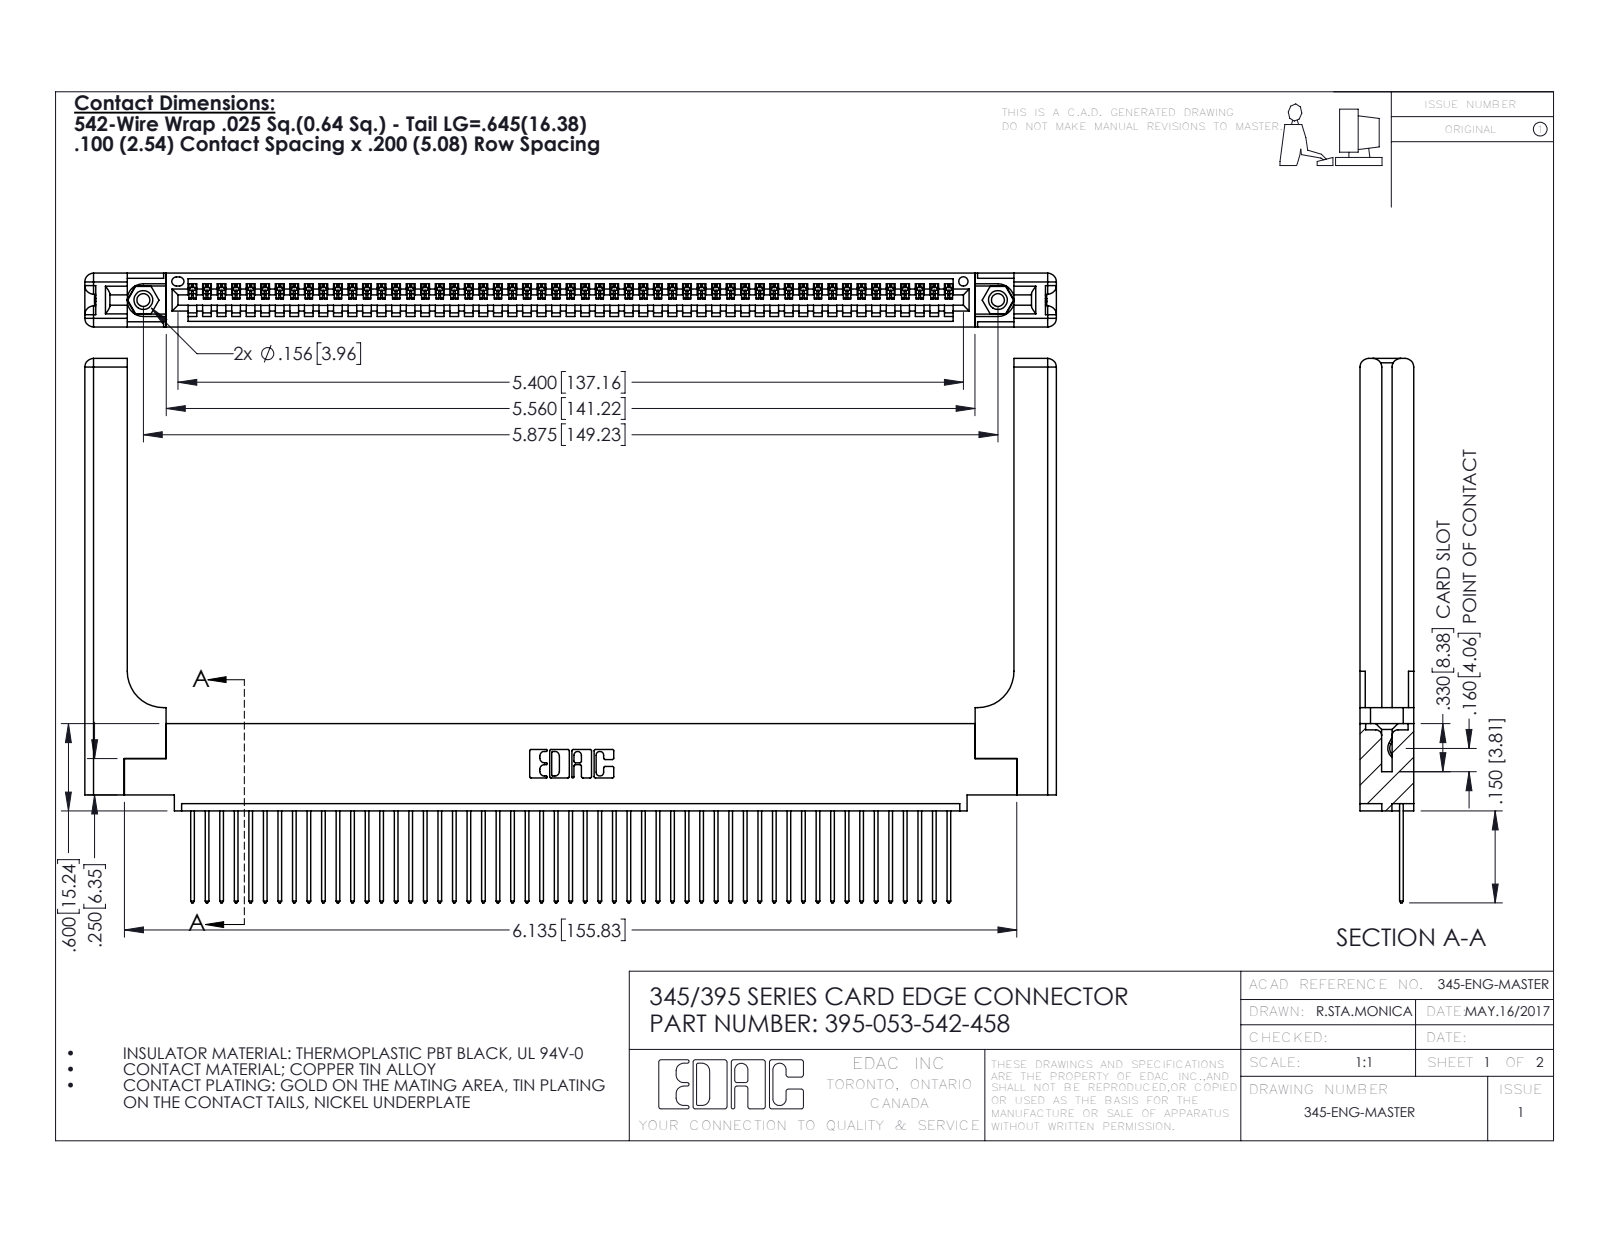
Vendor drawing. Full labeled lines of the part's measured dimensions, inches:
Part name (STEP PRODUCT): 395-053-542-458; 345-292-001_345-293-142; 345-250-001_345-250-001-102; 345 Part_0.110 Offset - 0.156 Dia-TH (+1 more)
STEP written by: SolidWorks 2016 (CONFIG_CONTROL_DESIGN)
Units: inches
Bodies: 58 solids, 3460 faces (2352 planar, 1048 cylindrical, 60 other)
Overall size (bounding box): 6.679 × 3.742 × 0.37
Volume: 1.511 in³ · Surface area: 43.21 in²
Round holes (diameter × count): ⌀0.089 ×2, ⌀0.125 ×2, ⌀0.156 ×2, ⌀0.064 ×1
Round bosses / shafts (diameter × count): ⌀0.155 ×2
Partial cylindrical surfaces — rounded edges, fillets, slot ends (radius × count): R0.006 ×106, R0.01 ×106, R0.01 ×22, R0.06 ×16, R0.007 ×6, R0.031 ×6, R0.026 ×3, R0.03 ×2
Main face-to-face distances: 0.072, 0.298, 0.37, 0.098, 0.272, 0.025, 0.2, 0.225, 0.148, 0.15
Hole centre spacings: 0.27, 5.639, 5.875
